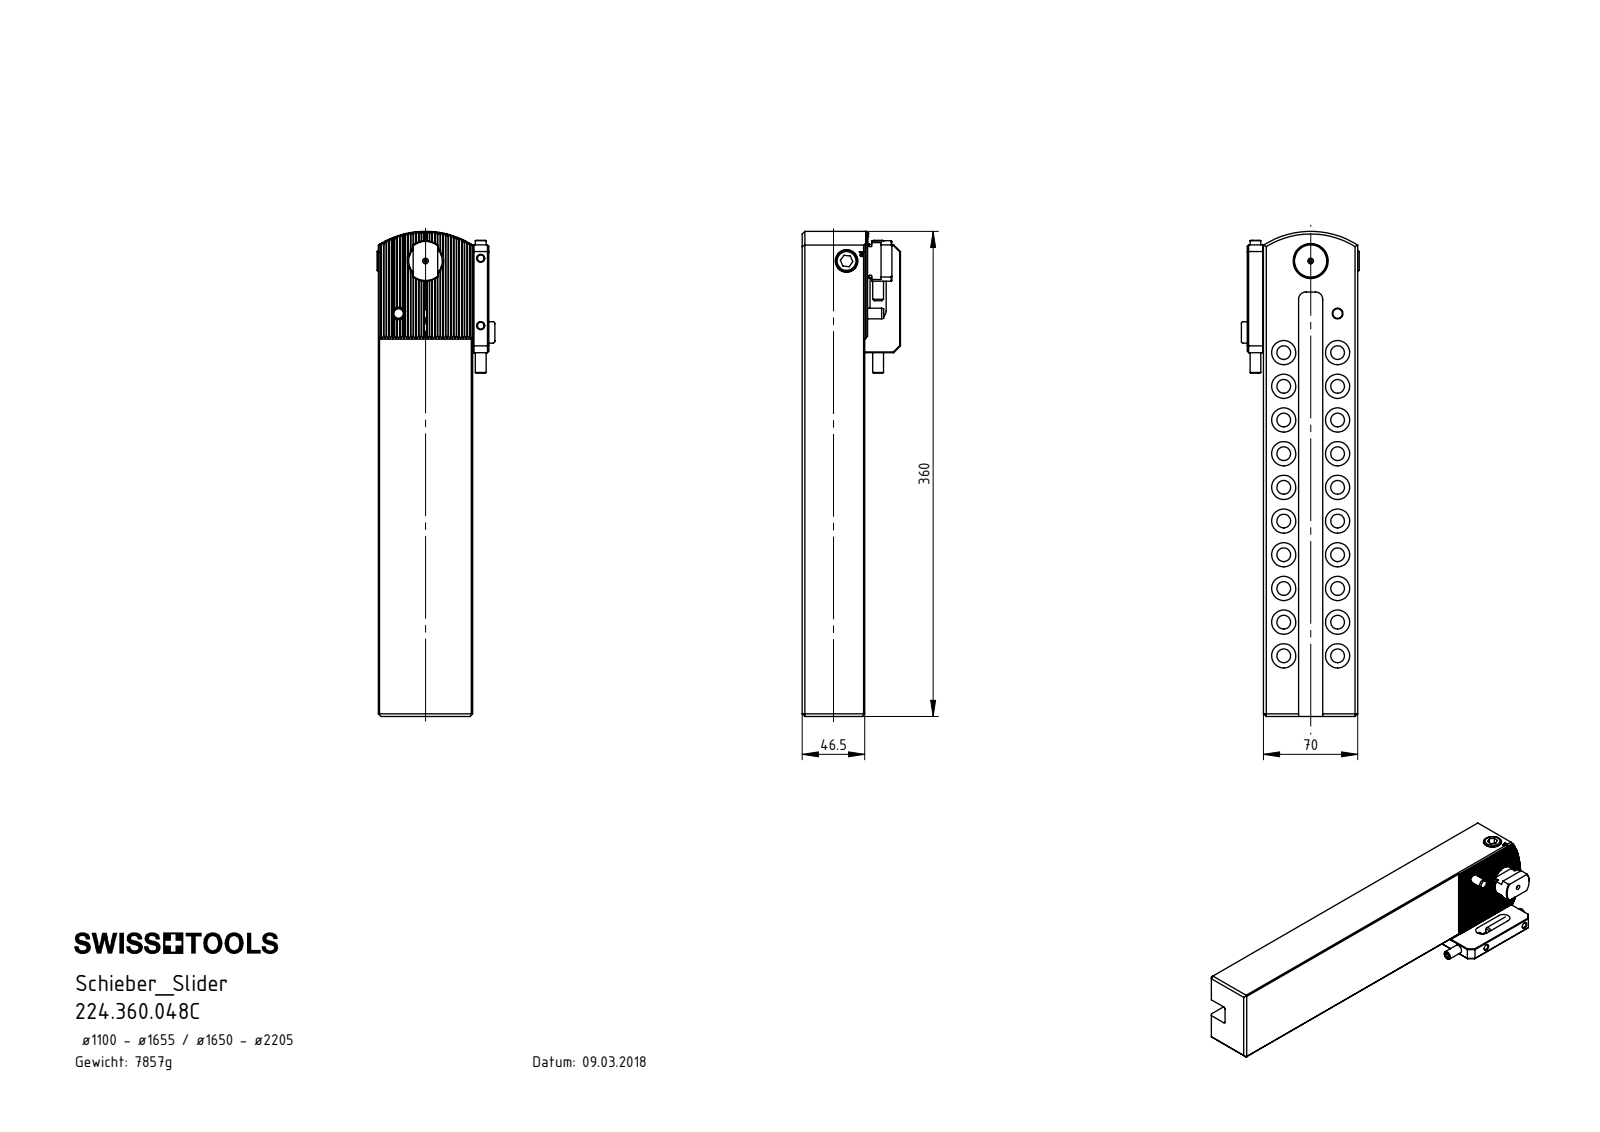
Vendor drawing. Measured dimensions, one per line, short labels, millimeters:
name: ISO 4026 - M8 x 45; ISO 4762 - M10 x 16; VK1-ER7.001.012_A; VK1-ER3.001.028_A (+6 more)
written by: SolidWorks 2017 (CONFIG_CONTROL_DESIGN)
unit: mm
bodies: 10 solids, 724 faces (319 planar, 247 cylindrical, 158 other)
size: 360 × 87.5 × 73
volume: 1 001 000 mm³; area: 162 838 mm²
holes: 21× ⌀18, 20× ⌀10.2, 2× ⌀5, 2× ⌀6, 2× ⌀6.8, 1× ⌀2, 1× ⌀8, 1× ⌀8.5, 1× ⌀10.5, 1× ⌀11, 1× ⌀14, 1× ⌀25
bosses: 2× ⌀16, 1× ⌀10, 1× ⌀8
rounds: 33× R0.14, 4× R2, 3× R1.5, 2× R5.5, 2× R6, 1× R12.3, 1× R15, 1× R65
face distances: 70, 46.5, 44, 26, 26.5, 18, 20, 6.5, 40, 13.5
hole spacings: 25, 47.17, 50, 64.03, 75, 85, 100, 107.7
